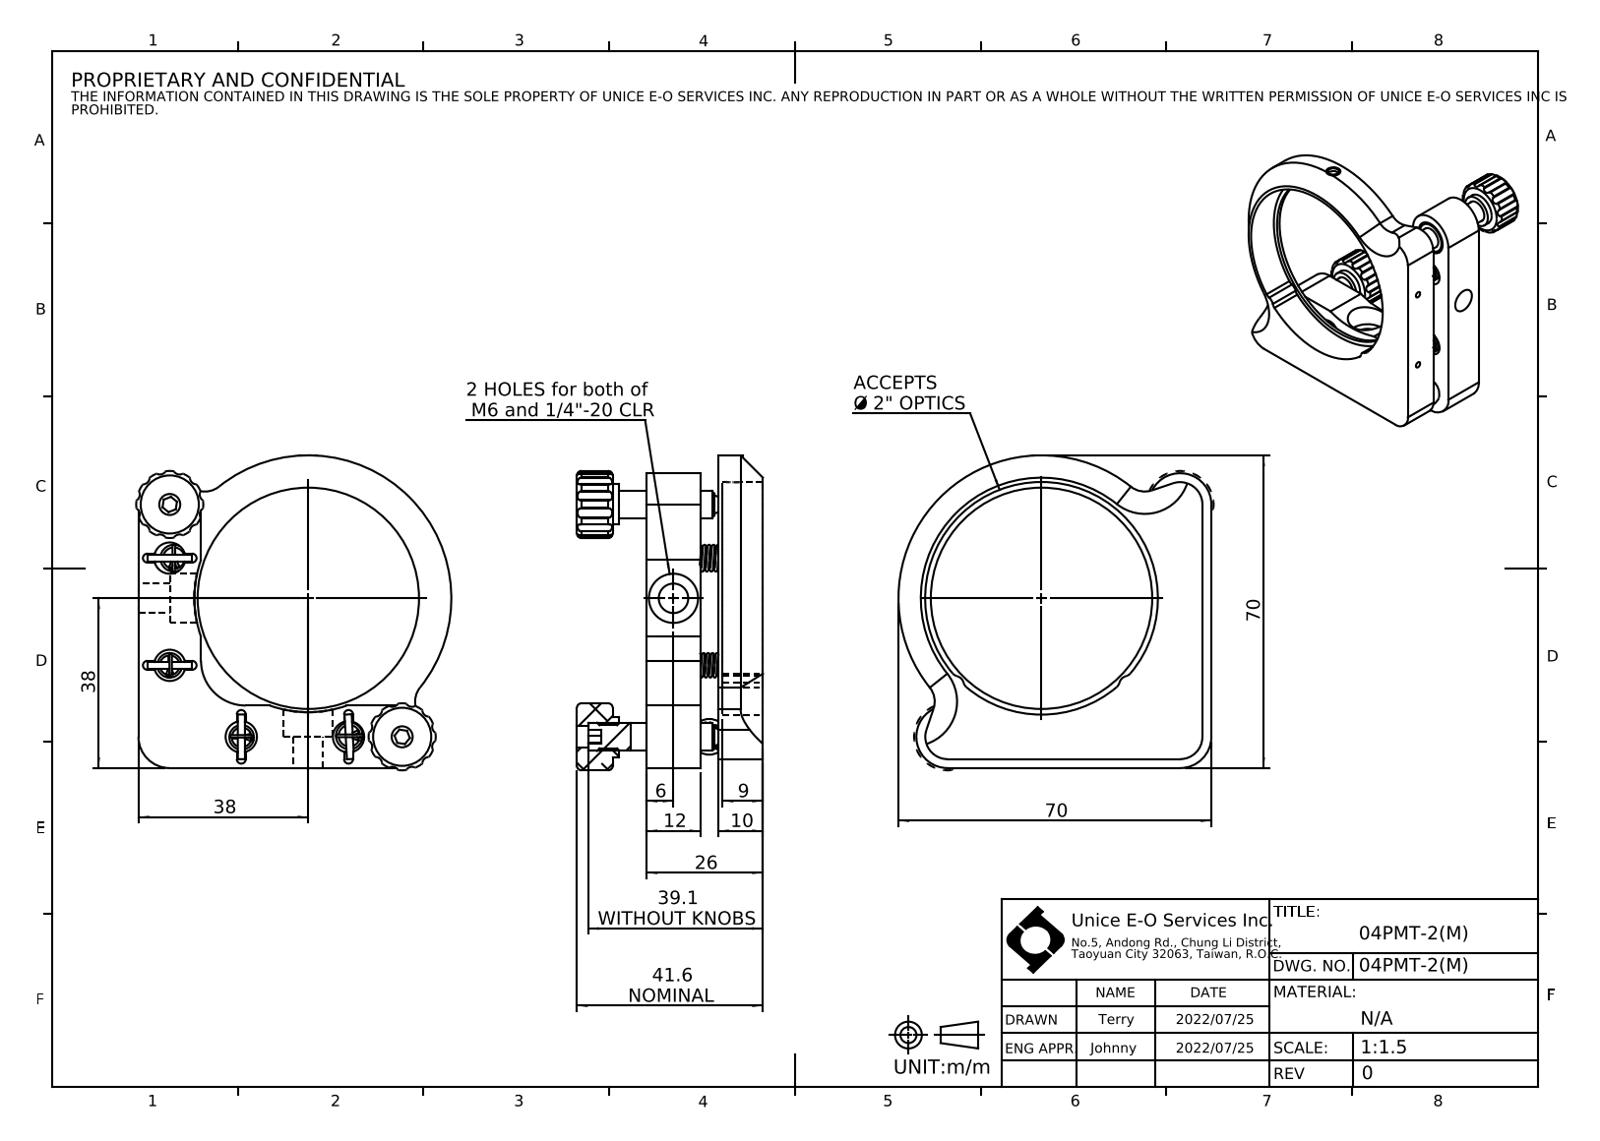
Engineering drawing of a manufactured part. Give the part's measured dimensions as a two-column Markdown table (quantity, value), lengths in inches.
| quantity | value |
| --- | --- |
| part name | 04PMT-2(M) |
| STEP written by | SolidWorks 2021 (AUTOMOTIVE_DESIGN) |
| units | inches |
| bodies | 21 solids, 487 faces (123 planar, 263 cylindrical, 101 other) |
| overall size | 2.776 × 2.776 × 1.638 |
| volume | 2.202 in³ |
| surface area | 36.67 in² |
| round holes (diameter × count) | 0.047 × 4, 0.067 × 4, 0.276 × 4, 0.157 × 2, 0.185 × 2, 0.204 × 2, 0.236 × 2, 0.248 × 2, 0.26 × 2, 0.374 × 2, 0.433 × 2, 0.13 × 1 |
| round bosses / shafts (diameter × count) | 0.024 × 6, 0.063 × 4, 0.022 × 4, 0.354 × 2, 0.236 × 1, 0.157 × 1, 0.098 × 1 |
| partial cylindrical surfaces (radius × count) | 0.012 × 48, 0.059 × 25, 0.039 × 8, 0.079 × 6, 0.197 × 5, 0.03 × 4, 0.276 × 3, 0.295 × 2 |
| main face-to-face distances | 0.551, 0.472, 0.394, 0.157, 1.024, 0.63, 0.079, 0.039, 0.354, 0.197 |
| hole center spacings | 0.945, 0.472, 0.723, 0.863, 1.238, 1.271, 1.356, 1.417 |
